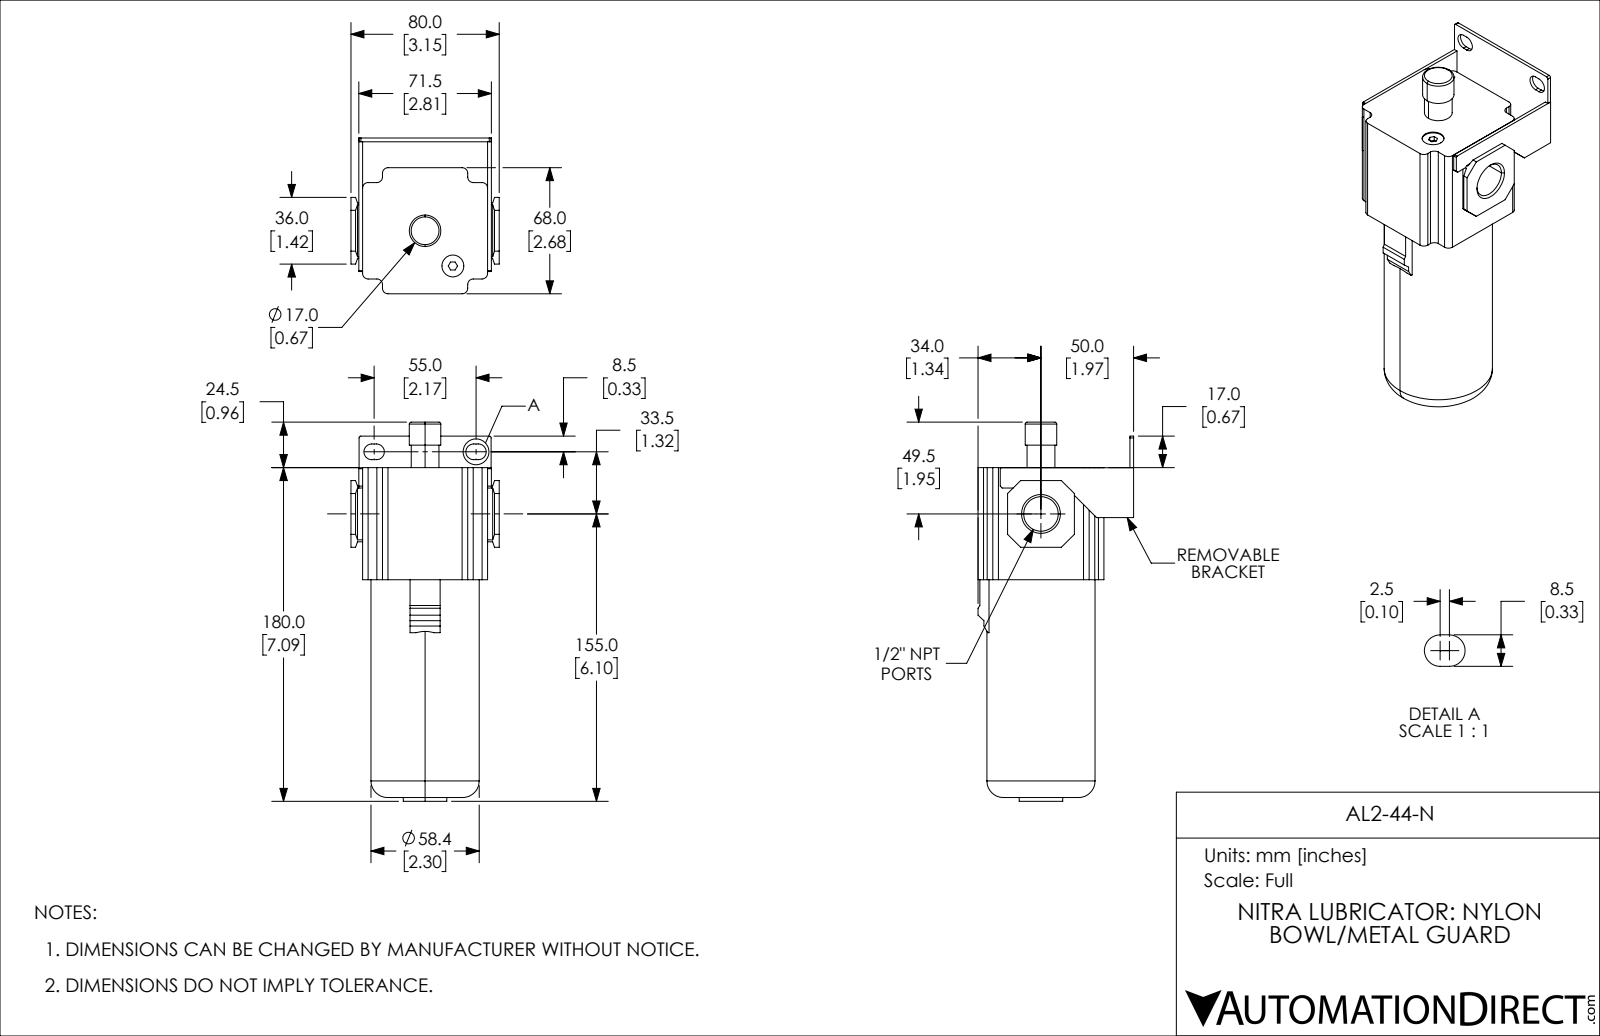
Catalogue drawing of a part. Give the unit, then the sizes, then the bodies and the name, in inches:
Units: inches
Overall size (bounding box): 8.051 × 3.307 × 3.15
Round holes (diameter × count): ⌀0.465 ×1, ⌀0.733 ×1
Round bosses / shafts (diameter × count): ⌀2.299 ×1, ⌀0.925 ×1, ⌀0.669 ×1, ⌀0.591 ×1
Partial cylindrical surfaces — rounded edges, fillets, slot ends (radius × count): R0.118 ×12, R0.167 ×4, R0.039 ×2
Main face-to-face distances: 0.079, 0.63, 2.677, 3.307, 3.228, 0.551, 2.736, 2.657, 0.167, 0.246
Volume: 35.86 in³ · Surface area: 94.3 in²
Bodies: 1 solid, 138 faces (98 planar, 32 cylindrical, 8 other)
Part name (STEP PRODUCT): AL2-44-N
STEP written by: SolidWorks 2019 (CONFIG_CONTROL_DESIGN)
